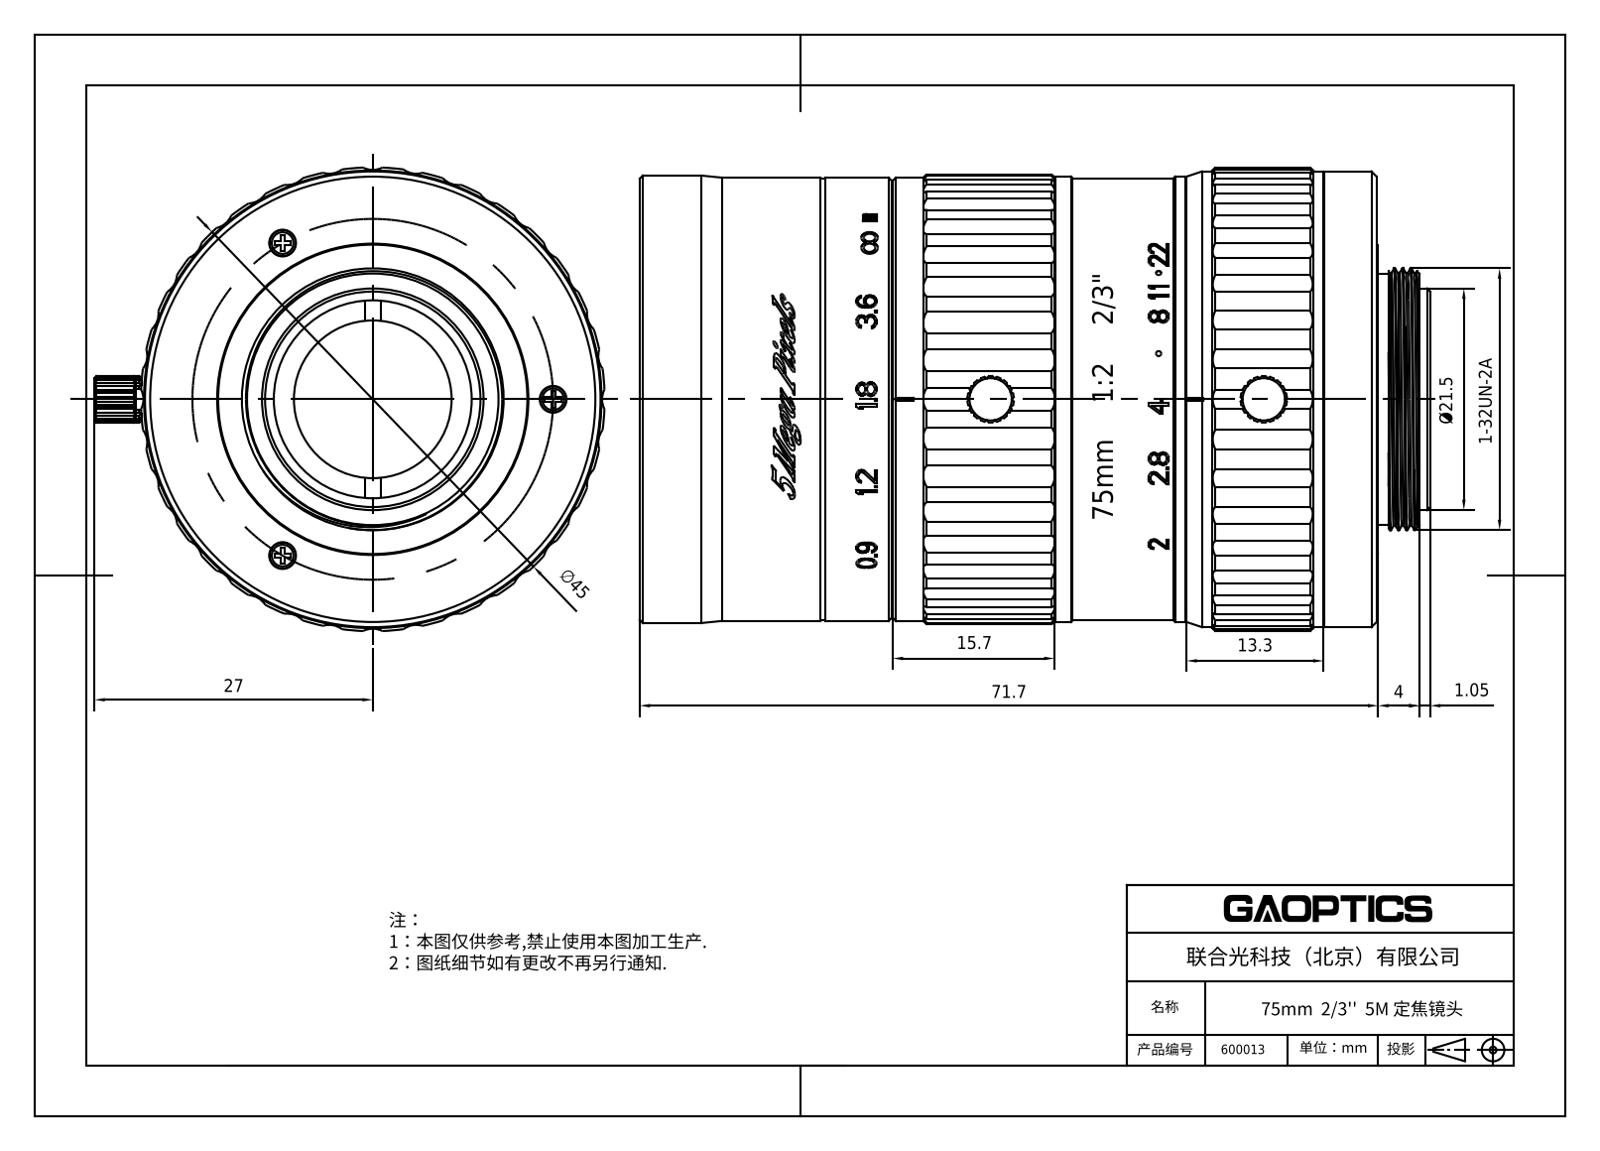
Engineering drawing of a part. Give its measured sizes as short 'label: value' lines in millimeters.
name: 600013
written by: SolidWorks 2020 (CONFIG_CONTROL_DESIGN)
unit: mm
bodies: 0 solids, 1288 faces (402 planar, 346 cylindrical, 540 other)
size: 76.7 × 49.48 × 44.96
holes: 3× ⌀2.6, 1× ⌀15.3, 1× ⌀17.6, 1× ⌀19.2, 1× ⌀20, 1× ⌀30.2, 1× ⌀37.2, 1× ⌀37.8, 1× ⌀38, 1× ⌀38.4, 1× ⌀39.8, 1× ⌀39.95
bosses: 3× ⌀2.5, 2× ⌀2, 1× ⌀44.2, 1× ⌀43.4, 1× ⌀43.2, 1× ⌀43, 1× ⌀42.9, 1× ⌀42.84
rounds: 72× R2, 3× R0.45, 2× R1, 2× R2.25, 1× R20.65, 1× R21.95, 1× R22.5
face distances: 4.6, 26.8, 12.7, 4.04, 4.19, 0.41, 4.45, 67.05, 67.46, 71.5
hole spacings: 17.5, 30.31, 30.32
